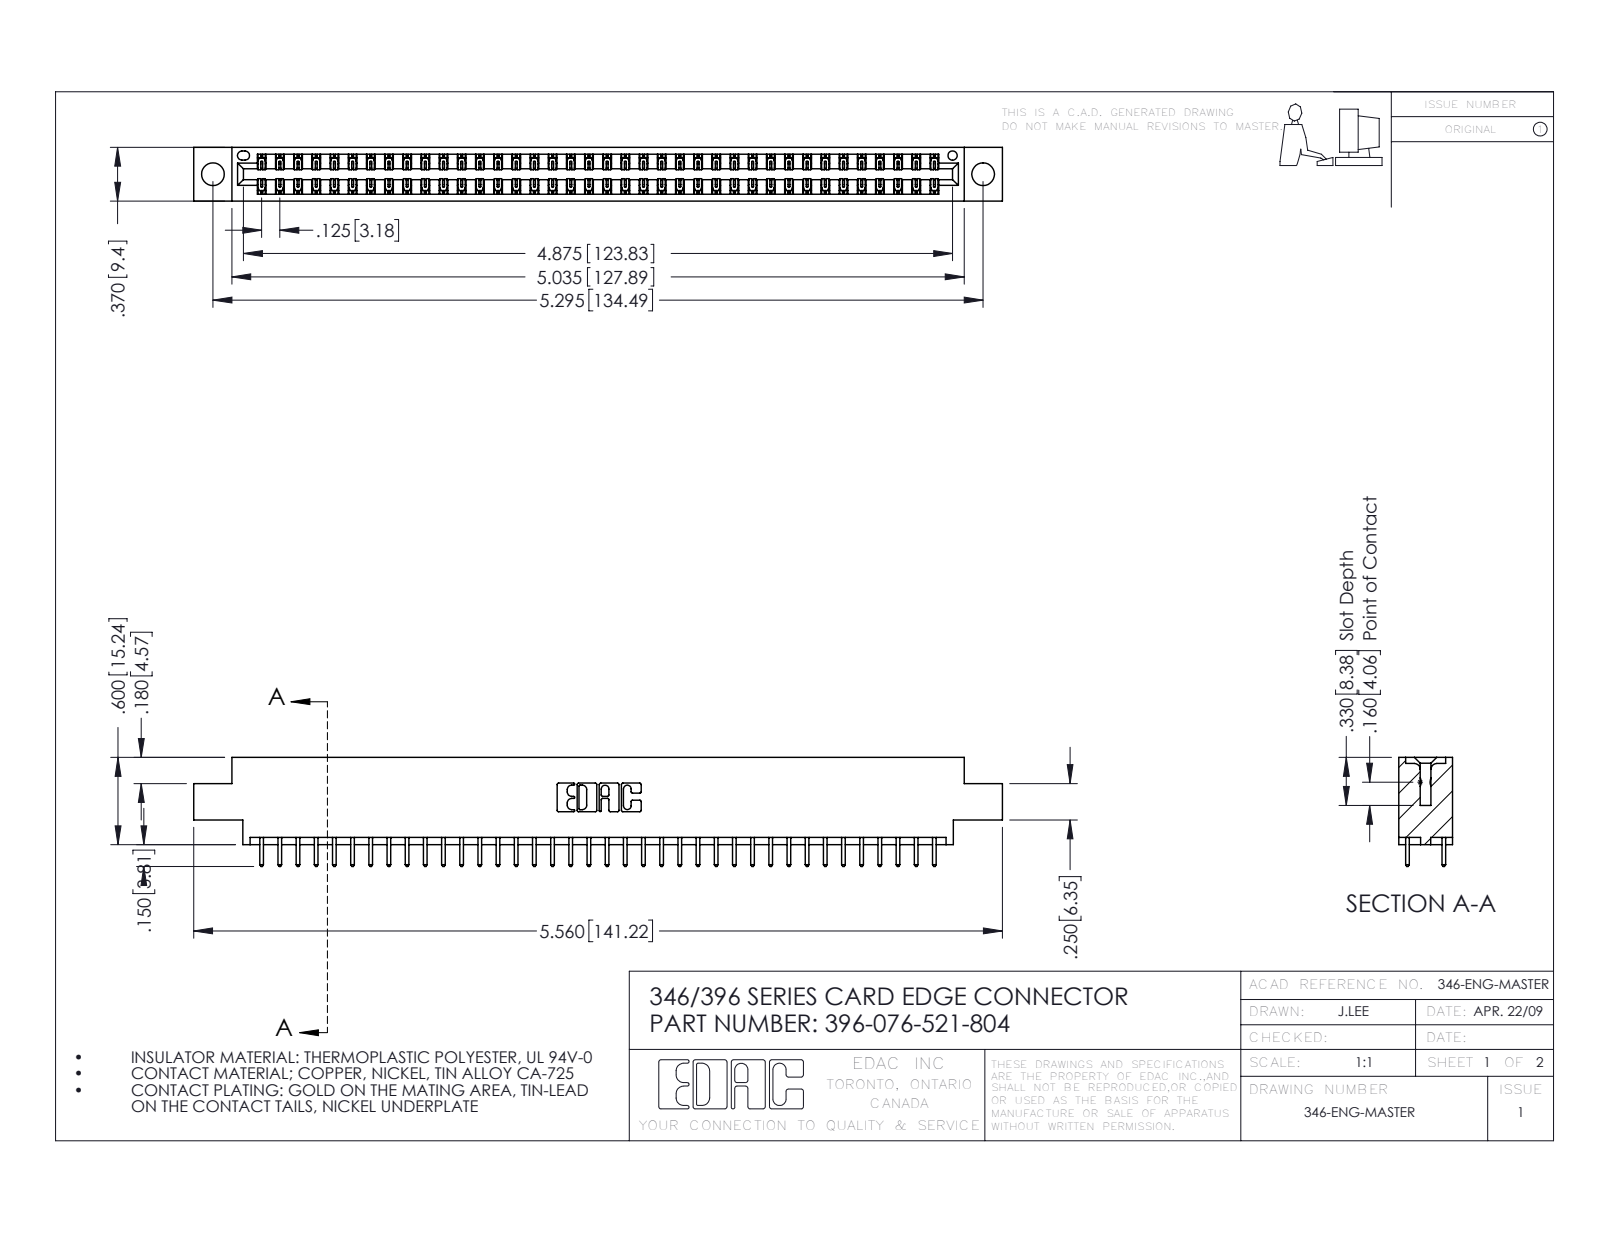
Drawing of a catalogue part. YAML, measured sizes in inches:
part_name: "346 Part_0.170 Offset - 0.156 Dia-TH; 345-292-001_345-293-121; 396-076-521-804"
step_written_by: "SolidWorks 2016 (CONFIG_CONTROL_DESIGN)"
units: inches
bodies: {solids: 77, faces: 4078, planar: 2740, cylindrical: 1338, other: 0}
overall_size: [5.56, 0.75, 0.37]
volume: 0.822
surface_area: 28.26
round_holes:
  - {diameter: 0.156, count: 2}
  - {diameter: 0.064, count: 1}
partial_cylinders:
  - {radius: 0.006, count: 114}
  - {radius: 0.01, count: 76}
  - {radius: 0.01, count: 22}
  - {radius: 0.007, count: 6}
  - {radius: 0.031, count: 6}
  - {radius: 0.026, count: 3}
  - {radius: 0.014, count: 2}
  - {radius: 0.022, count: 2}
face_to_face_distances: [0.048, 0.322, 0.37, 0.25, 0.072, 0.298, 0.025, 0.275, 0.148, 0.222]
hole_center_spacings: [0.246, 5.086, 5.295]
